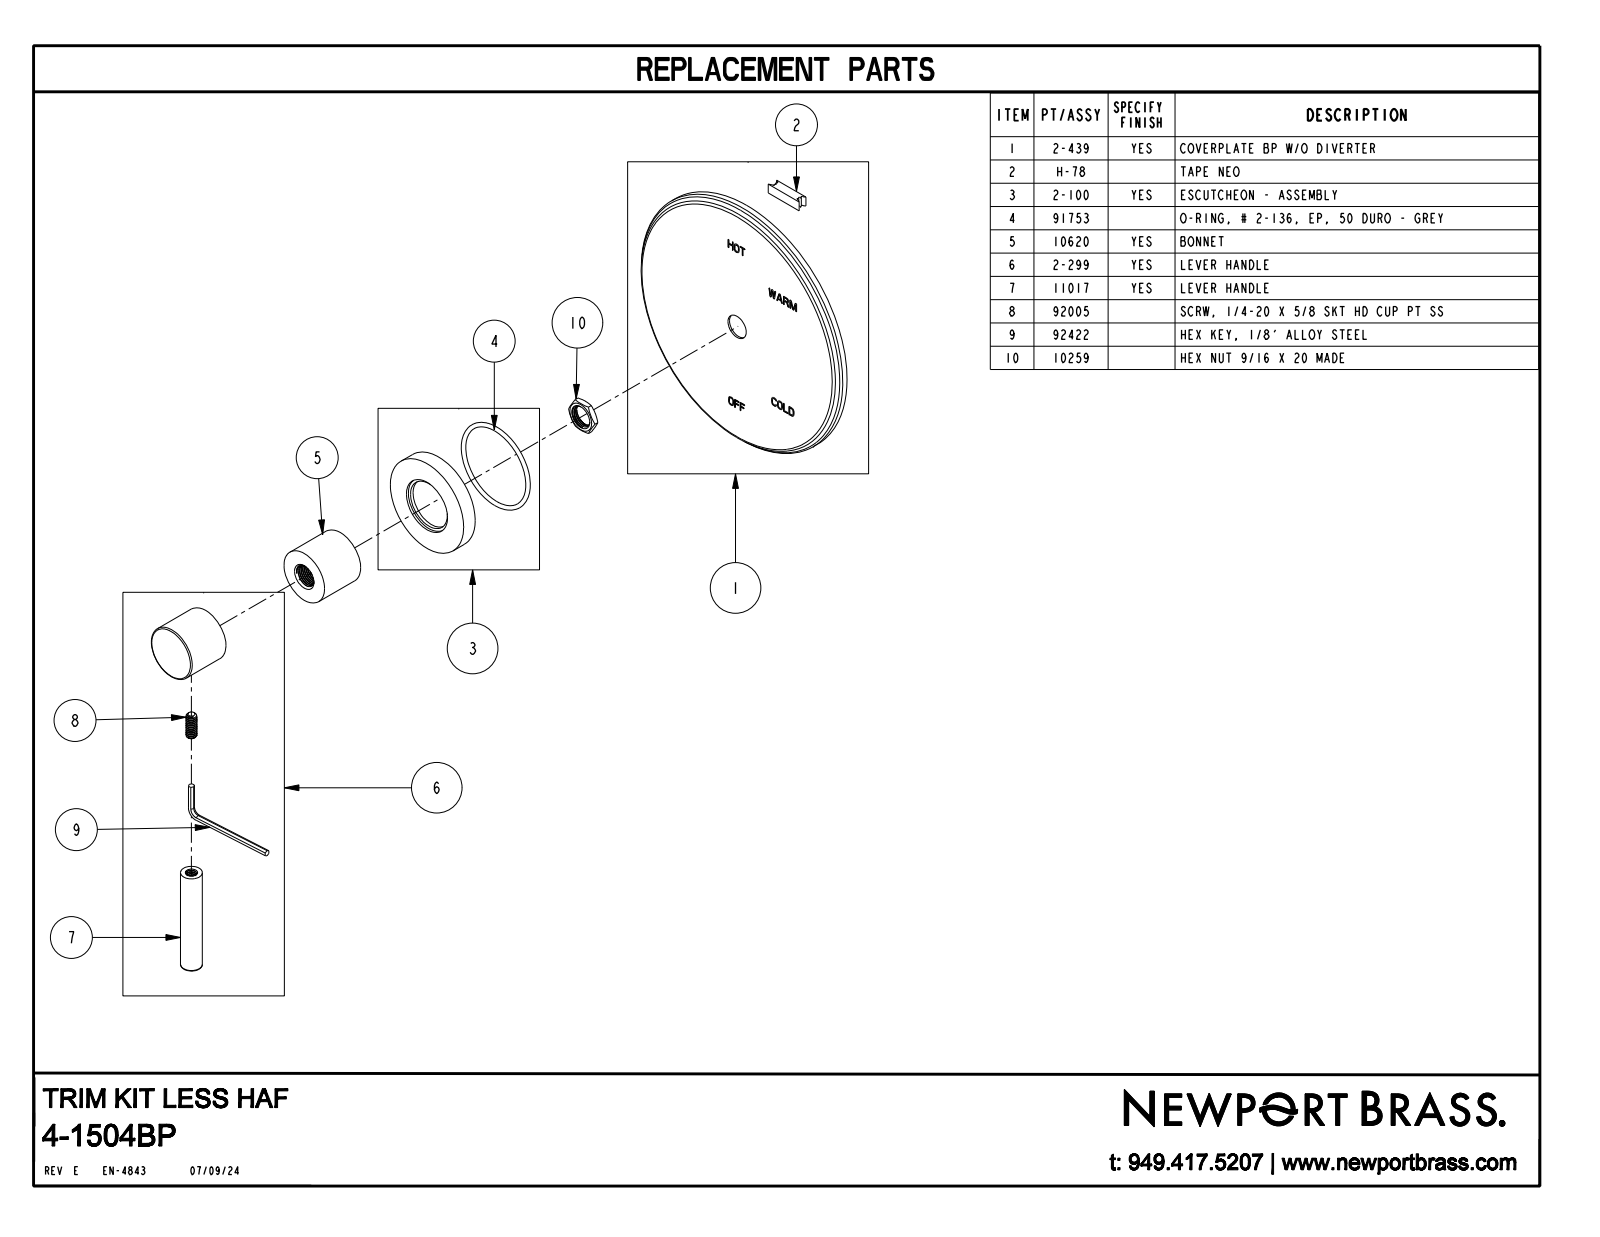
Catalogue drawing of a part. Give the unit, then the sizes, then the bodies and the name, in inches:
Units: inches
Overall size (bounding box): 6.5 × 6.5 × 2.936
Round holes (diameter × count): ⌀0.52 ×1
Round bosses / shafts (diameter × count): ⌀6.5 ×1, ⌀2.375 ×1, ⌀1.313 ×1, ⌀1.312 ×1, ⌀0.5 ×1, ⌀0.4 ×1
Main face-to-face distances: 0.313, 0.688, 0.375, 0.02, 1.503, 2.936, 2.623, 2.248, 1.796, 1.483
Volume: 15.28 in³ · Surface area: 89.57 in²
Bodies: 1 solid, 359 faces (335 planar, 14 cylindrical, 10 other)
Part name (STEP PRODUCT): 4-1504BP
STEP written by: CREO PARAMETRIC BY PTC INC, 2018400 (CONFIG_CONTROL_DESIGN)
